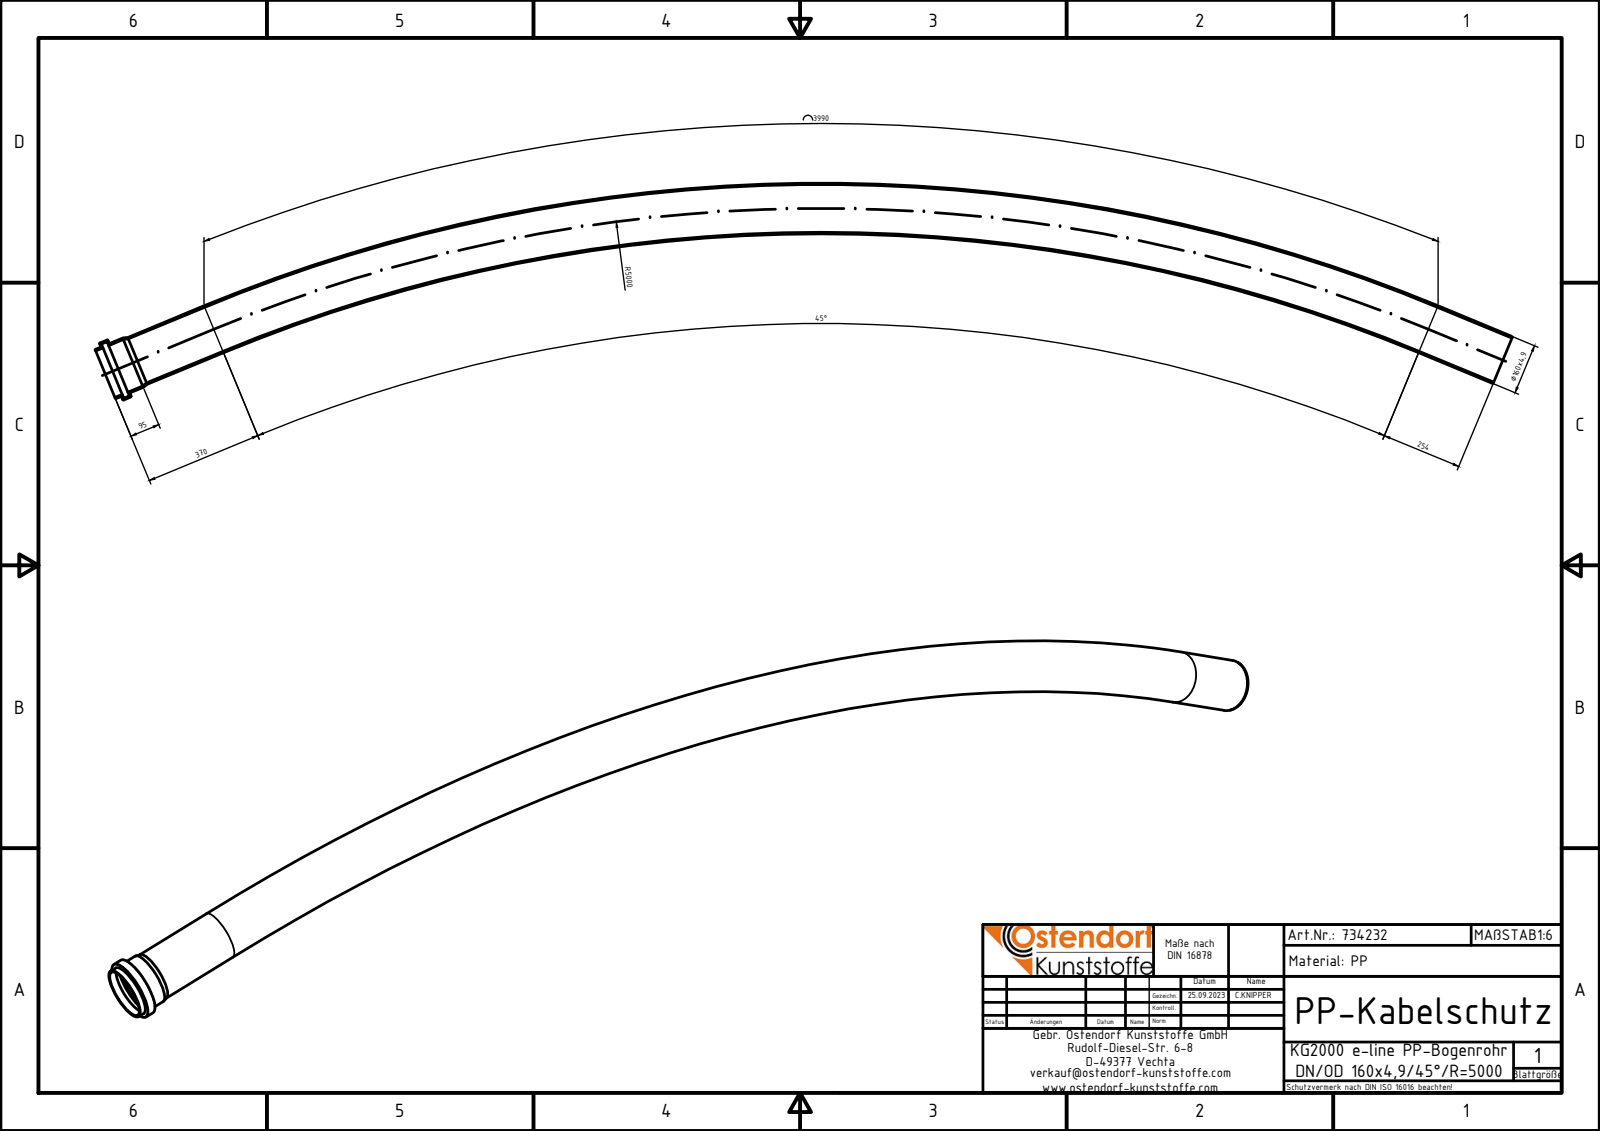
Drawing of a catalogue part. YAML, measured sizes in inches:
part_name: "734232z"
step_written_by: "Autodesk Inventor 2024 (AUTOMOTIVE_DESIGN)"
units: inches
bodies: {solids: 1, faces: 23, planar: 6, cylindrical: 10, other: 7}
overall_size: [175.813, 26.92, 7.657]
volume: 668.8
surface_area: 6939
round_holes:
  - {diameter: 5.913, count: 2}
  - {diameter: 6.24, count: 2}
  - {diameter: 7.272, count: 1}
round_bosses_or_shafts:
  - {diameter: 6.626, count: 2}
  - {diameter: 6.299, count: 2}
  - {diameter: 7.657, count: 1}
face_to_face_distances: [0.193, 0.949, 0.756, 1.142, 0.787, 0.98, 1.737, 1.93]
